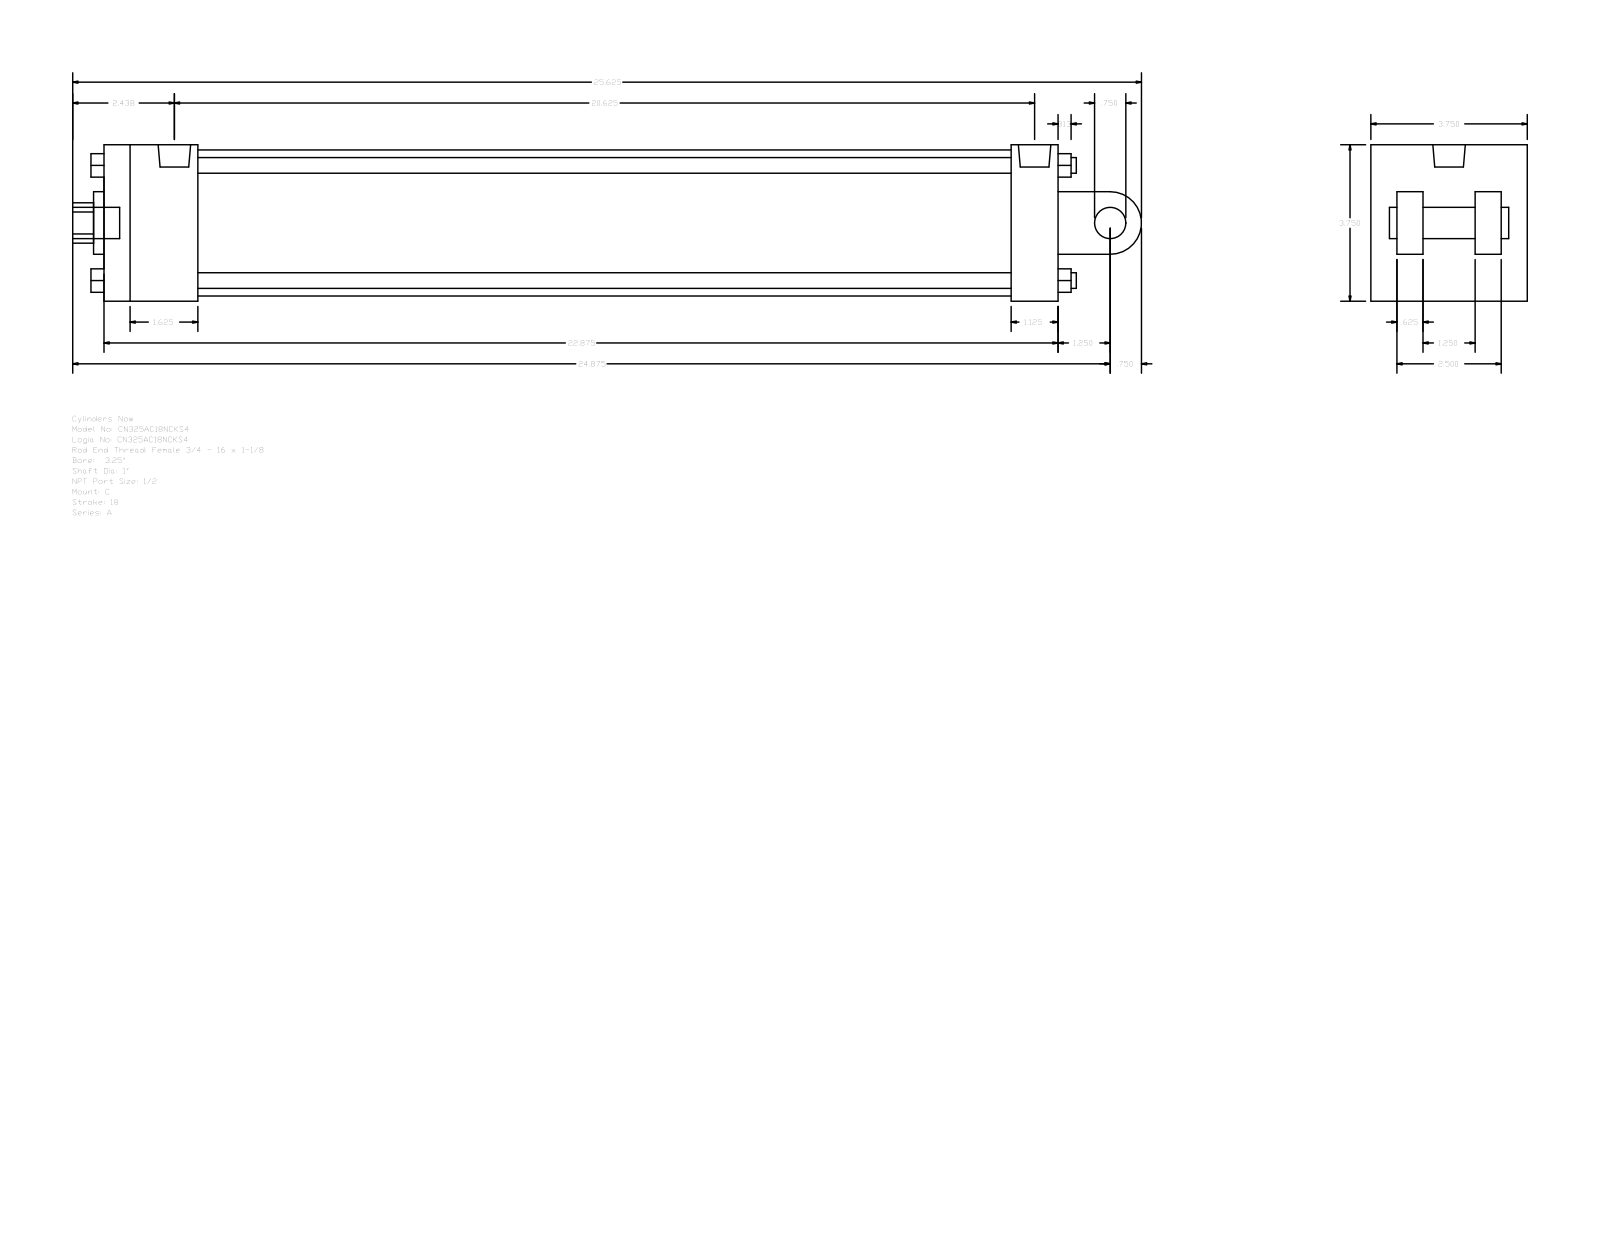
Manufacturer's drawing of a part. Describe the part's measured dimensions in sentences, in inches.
The part is named "A_C__0325_1". Its 3-D file was written by "GSSL Pune (CONFIG_CONTROL_DESIGN)". It is 0 solids with 135 faces: 102 planar, 33 cylindrical and 0 other. Overall it measures 25.625 by 3.75 by 3.75 inches. Round holes: 2 of diameter 0.344, 1 of diameter 0.778, 1 of diameter 1, 1 of diameter 1.5, 1 of diameter 3.5. Round bosses or shafts: 4 of diameter 0.375, 2 of diameter 0.75, 2 of diameter 0.344, 1 of diameter 0.778. Partial cylindrical surfaces (rounded edges, fillets, slot ends): 1 of radius 0.484, 1 of radius 0.75. The main face-to-face distances are 3.75, 22.875, 0.625, 2.5, 1.875, 1.25, 3.125, 2.625, 21.75, 1.125. The hole center spacings are 0.125.
